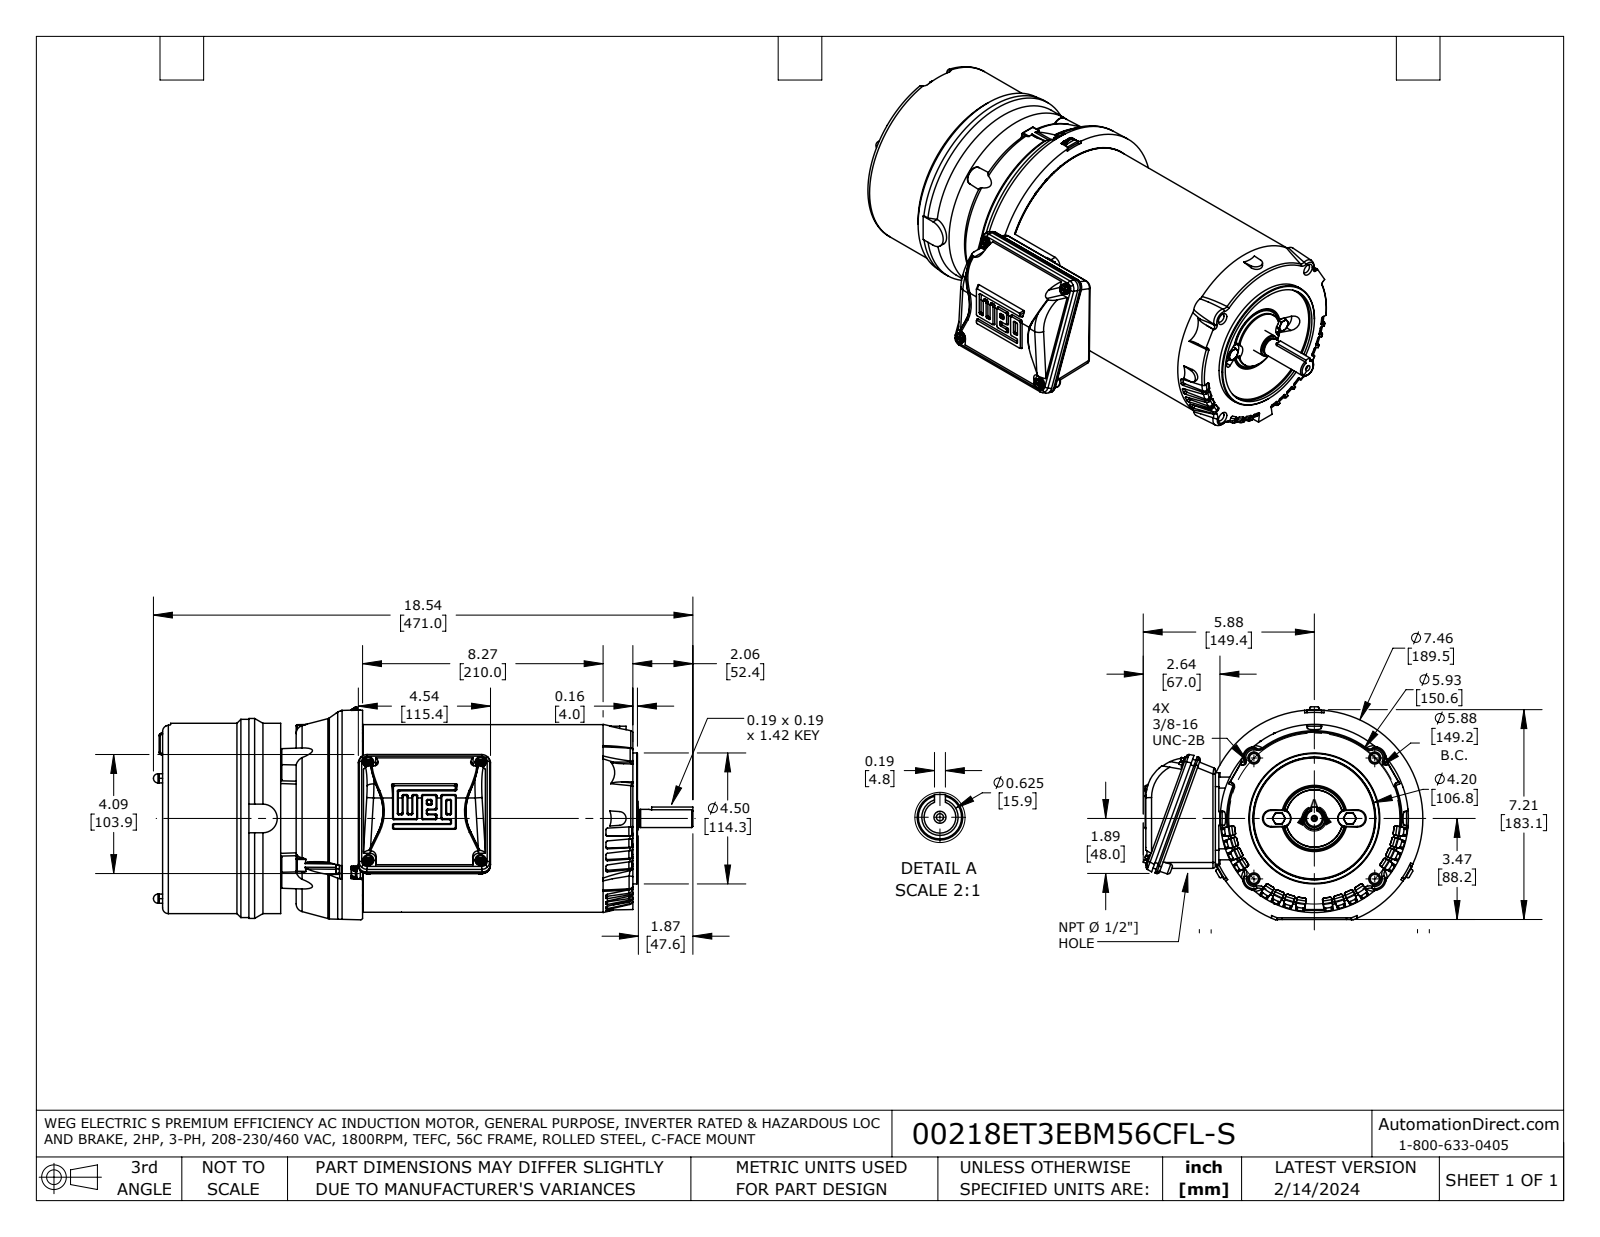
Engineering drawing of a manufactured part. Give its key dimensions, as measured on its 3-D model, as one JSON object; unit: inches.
{"part_name": "00218ET3EBM56CFL-S", "step_written_by": "SolidWorks 2021 (AUTOMOTIVE_DESIGN)", "units": "inches", "bodies": {"solids": 15, "faces": 1404, "planar": 534, "cylindrical": 353, "other": 517}, "overall_size": [18.543, 9.612, 7.319], "volume_in3": 563.8, "surface_area_in2": 779.9, "round_holes": [[0.313, 4], [0.124, 1]], "round_bosses_or_shafts": [[0.374, 4], [0.315, 3], [0.256, 3], [0.35, 2], [6.87, 1], [6.811, 1], [6.54, 1], [6.457, 1]], "partial_cylinders_radius": [[0.039, 51], [0.047, 40], [0.051, 32], [0.02, 16], [0.079, 12], [0.087, 12], [0.205, 8], [0.276, 8]], "face_to_face_distances": [8.248, 11.082, 2.835, 4.059, 6.894, 15.141, 4.591, 0.531, 2.303, 10.551], "hole_center_spacings": [2.937, 4.154, 5.874]}
